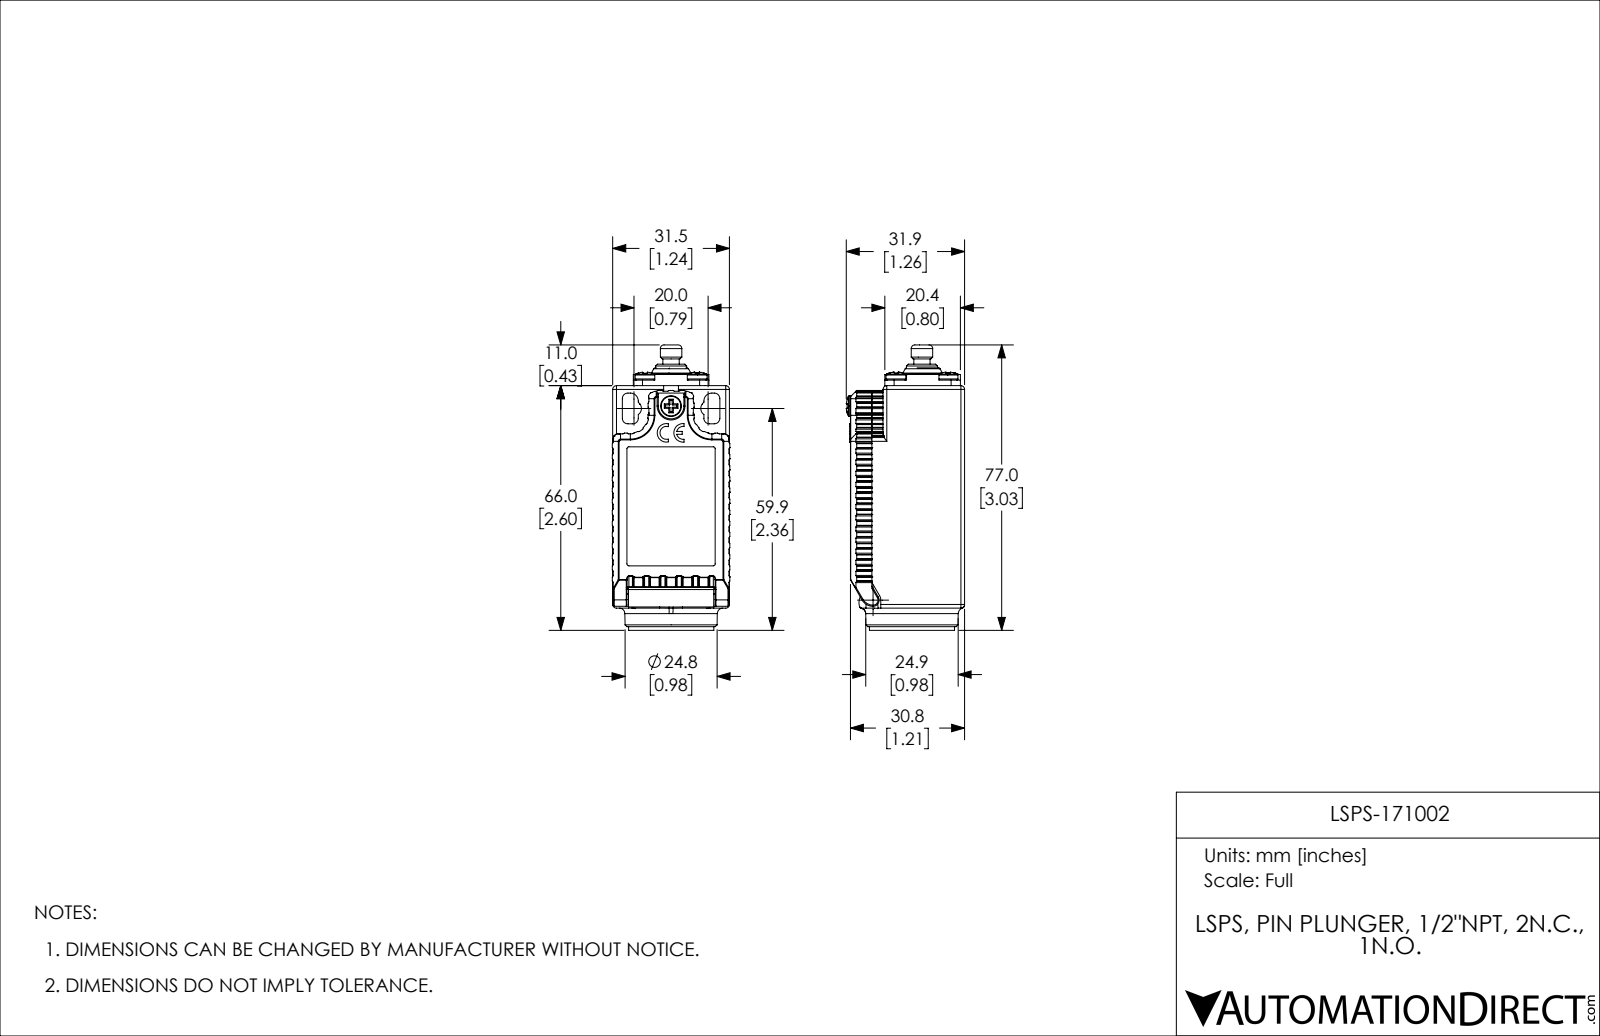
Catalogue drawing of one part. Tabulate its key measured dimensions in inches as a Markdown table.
| quantity | value |
| --- | --- |
| part name | 171-LSPS-Pin Plunger (step format) |
| STEP written by | SolidWorks 2013 (CONFIG_CONTROL_DESIGN) |
| units | inches |
| bodies | 12 solids, 2183 faces (972 planar, 902 cylindrical, 309 other) |
| overall size | 3.031 × 1.257 × 1.248 |
| volume | 1.566 in³ |
| surface area | 39.86 in² |
| round holes (diameter × count) | 0.091 × 5, 0.13 × 4, 0.217 × 4, 0.157 × 2, 0.146 × 1, 0.197 × 1, 0.315 × 1, 0.394 × 1, 0.512 × 1, 0.614 × 1, 0.638 × 1 |
| round bosses / shafts (diameter × count) | 0.067 × 5, 0.213 × 4, 0.906 × 1, 0.717 × 1, 0.618 × 1, 0.591 × 1, 0.441 × 1, 0.425 × 1 |
| partial cylindrical surfaces (radius × count) | 0.02 × 109, 0.008 × 108, 0.004 × 94, 0.013 × 32, 0.012 × 31, 0.039 × 19, 0.079 × 14, 0.098 × 12 |
| main face-to-face distances | 0.089, 1.152, 1.24, 0.063, 0.039, 1.102, 0.118, 0.102, 1.063, 1.165 |
| hole center spacings | 0.551, 0.39, 0.385, 0.395, 0.306, 0.646, 0.78, 0.787 |
